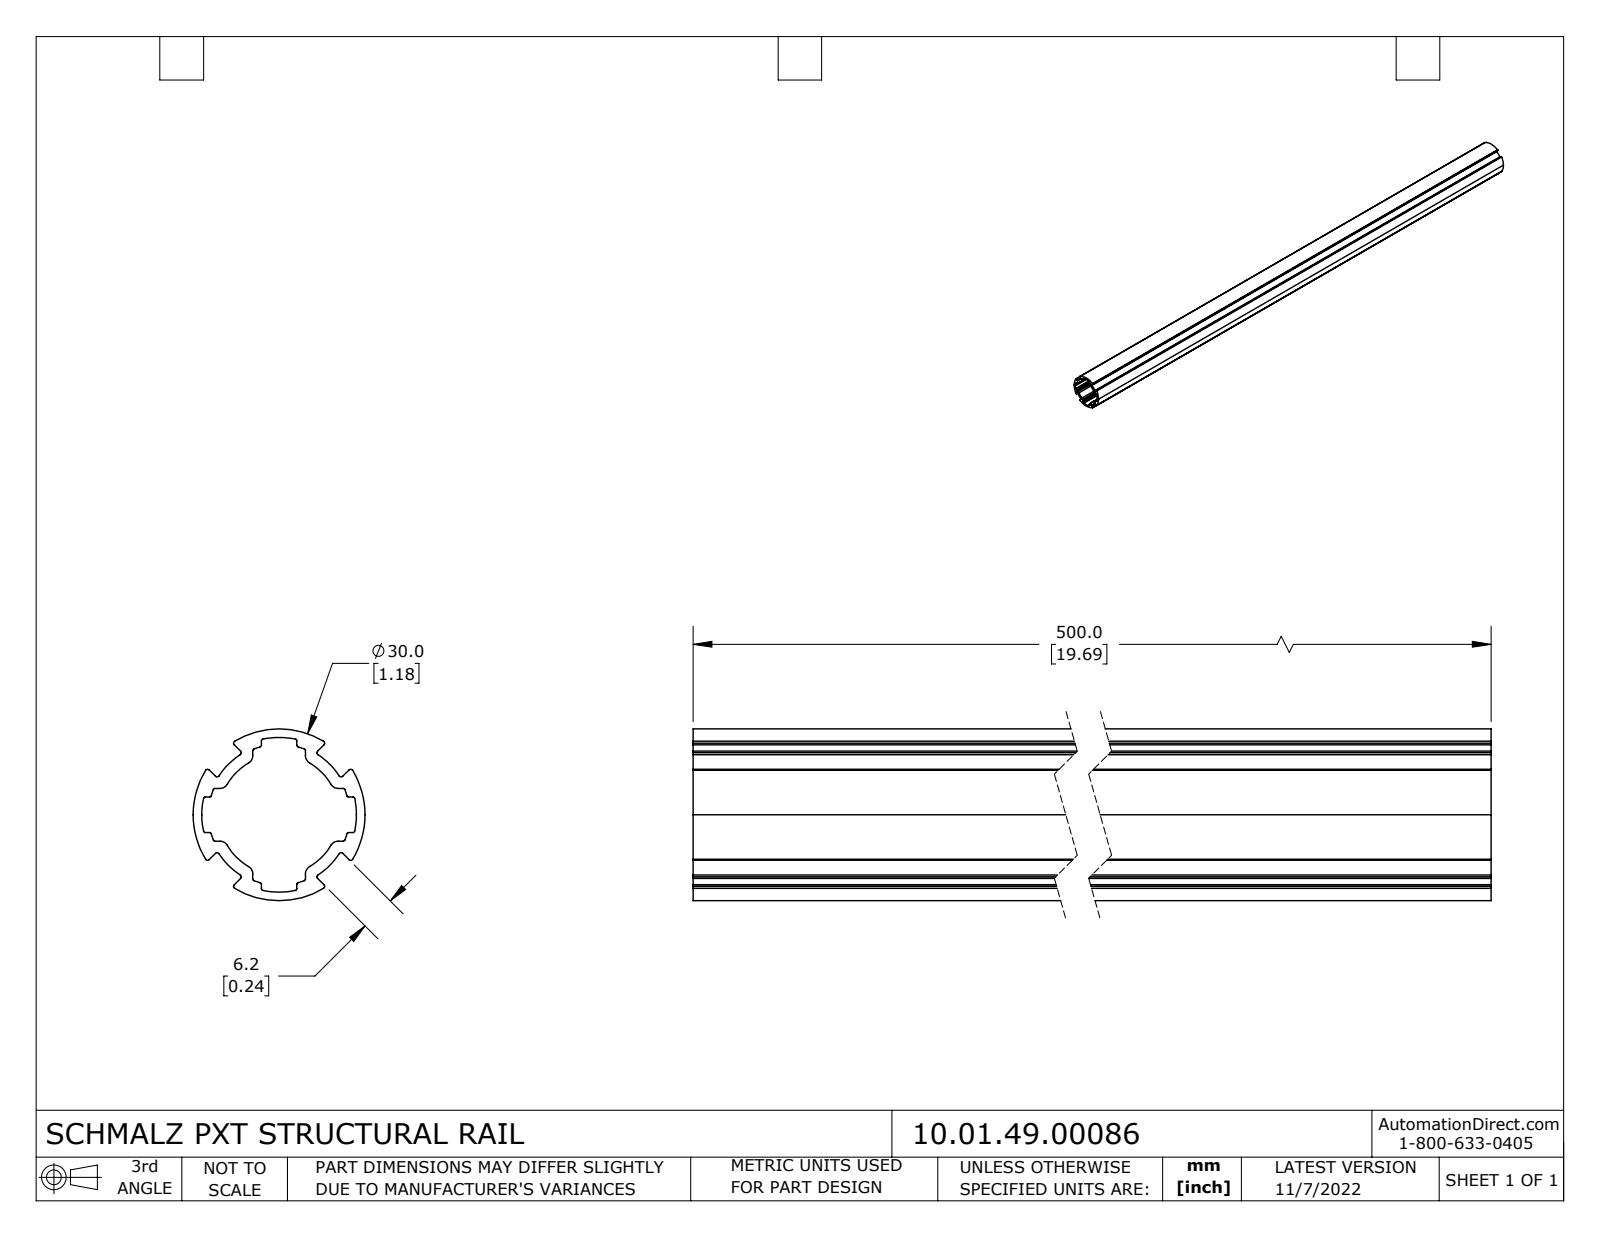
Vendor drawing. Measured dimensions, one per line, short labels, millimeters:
name: 10.01.49.00086
written by: SolidWorks 2021 (CONFIG_CONTROL_DESIGN)
unit: mm
bodies: 1 solid, 110 faces (26 planar, 84 cylindrical, 0 other)
size: 500 × 30 × 30
volume: 99 375 mm³; area: 99 652 mm²
rounds: 24× R0.3, 16× R0.4, 8× R1.5, 1× R10.5, 1× R12.3, 1× R12.5, 1× R13.5, 1× R15
face distances: 6.2, 1.5, 7.7, 9.2, 500
